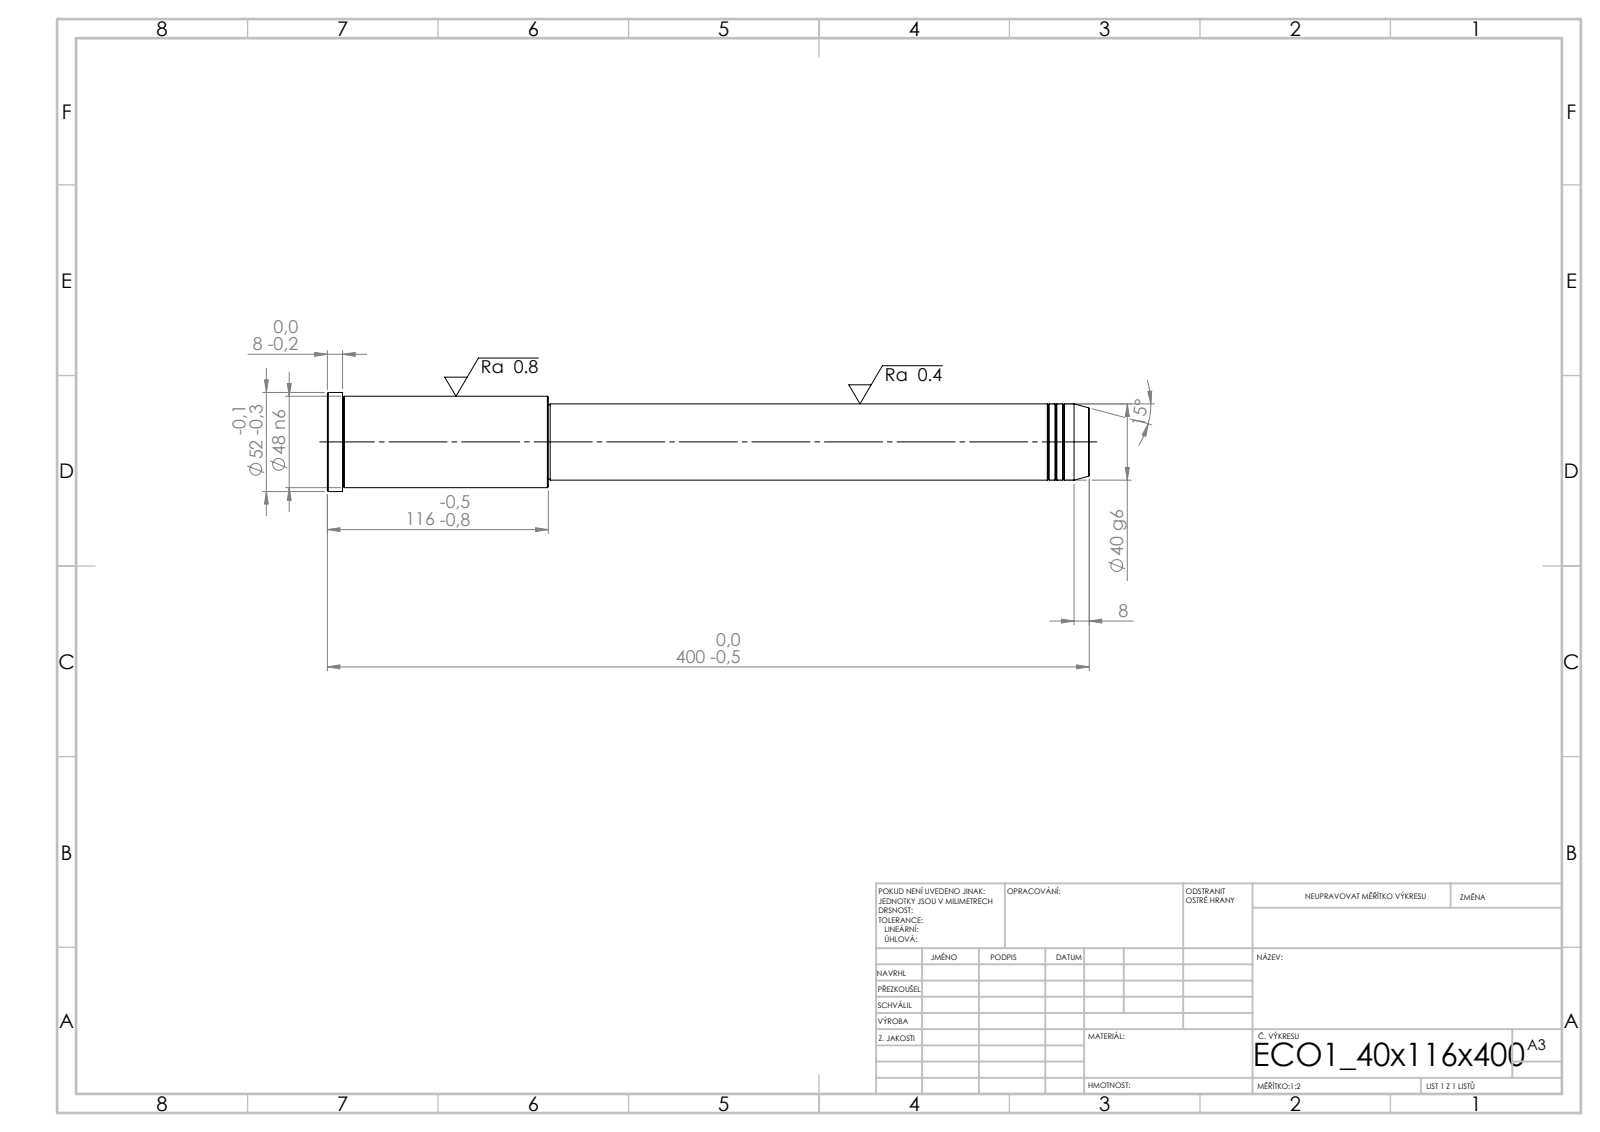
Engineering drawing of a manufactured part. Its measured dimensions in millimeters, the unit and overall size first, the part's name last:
Units: millimetres
Overall size (bounding box): 400 × 52 × 52
Round bosses / shafts (diameter × count): ⌀52 ×1, ⌀48 ×1, ⌀40 ×1, ⌀39 ×1
Main face-to-face distances: 400, 284, 116, 392, 108, 8, 283, 1, 109, 117
Volume: 567 958 mm³ · Surface area: 57 558 mm²
Bodies: 1 solid, 43 faces (5 planar, 14 cylindrical, 24 other)
STEP written by: SolidWorks 2019 (CONFIG_CONTROL_DESIGN)
